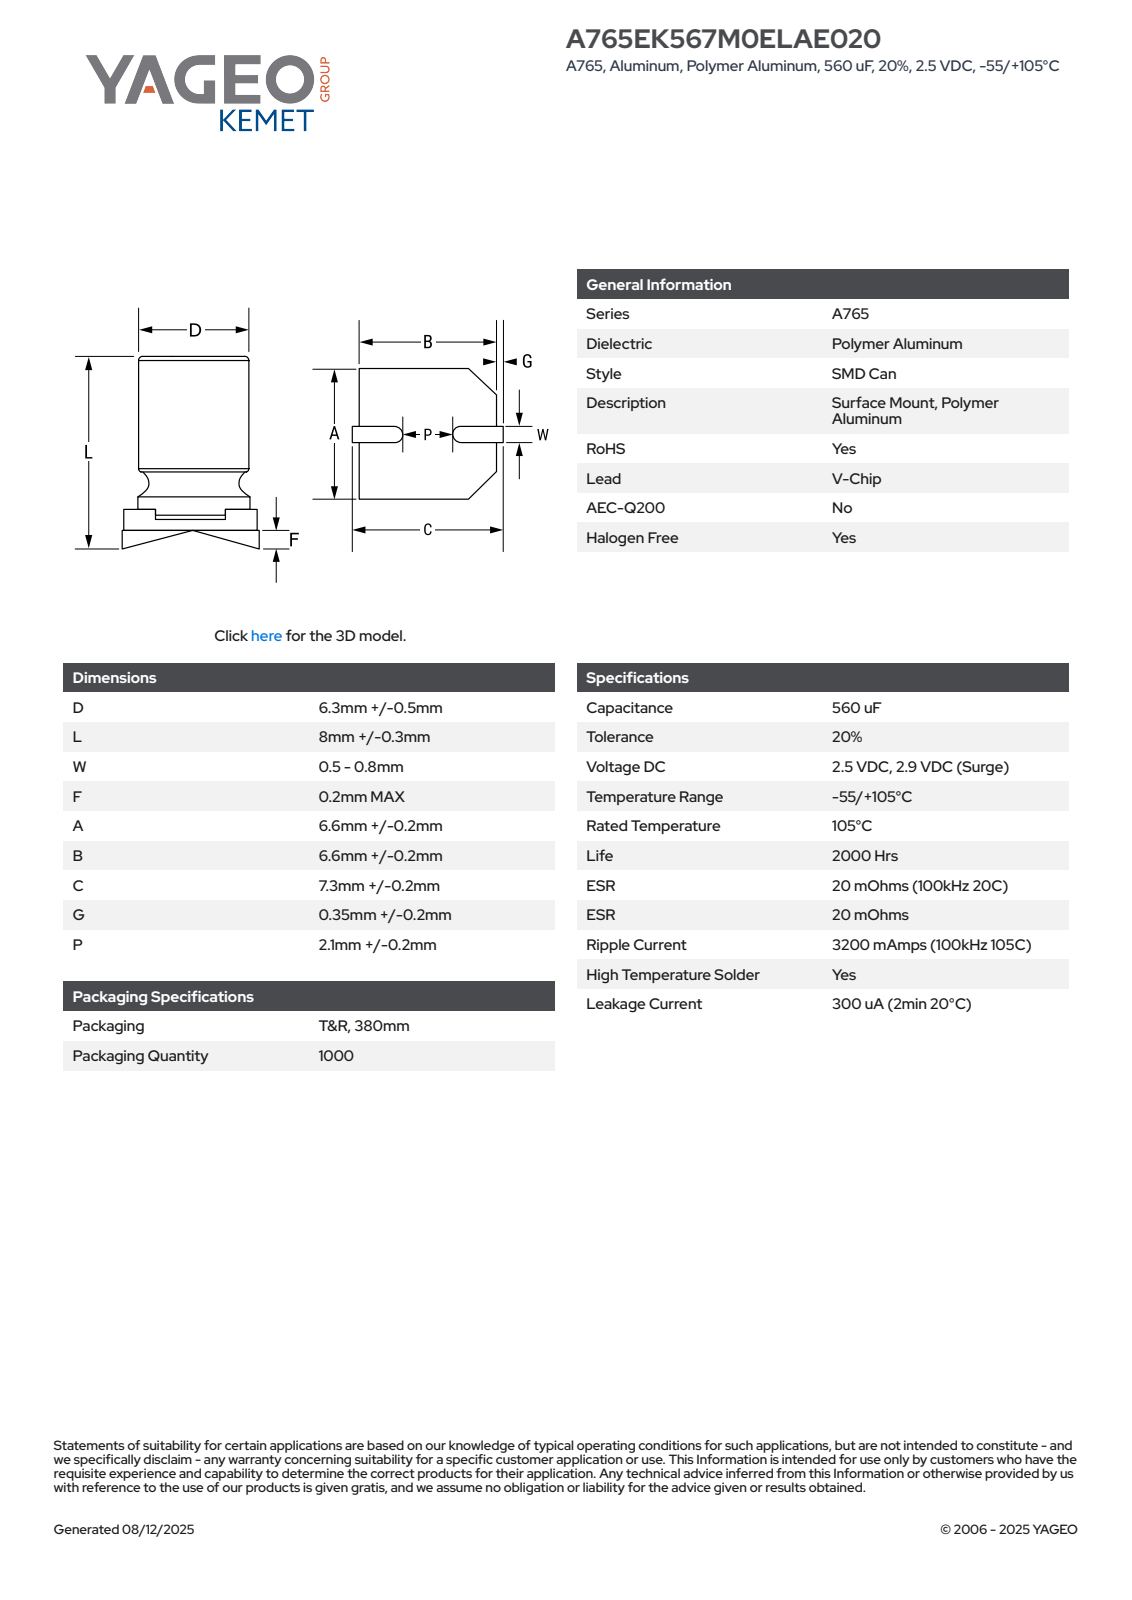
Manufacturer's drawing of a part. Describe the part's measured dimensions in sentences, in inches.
The part is named "CAC_KS_6.3X8_D6.8L8.3W0.8F0.2A6.8B6.8C7.5P2.3". Its 3-D file was written by "SolidWorks 2014 (AUTOMOTIVE_DESIGN)". It is 5 solids with 76 faces: 59 planar, 11 cylindrical and 6 other. Overall it measures 0.327 by 0.295 by 0.268 inches. Its volume is 0.017 cubic inches and its surface area 0.569 square inches. Round bosses or shafts: 1 of diameter 0.256. Partial cylindrical surfaces (rounded edges, fillets, slot ends): 2 of radius 0.008, 1 of radius 0.106, 1 of radius 0.134. The main face-to-face distances are 0.016, 0.319, 0.303, 0.319, 0.303, 0.268, 0.066, 0.082, 0.237, 0.237.
